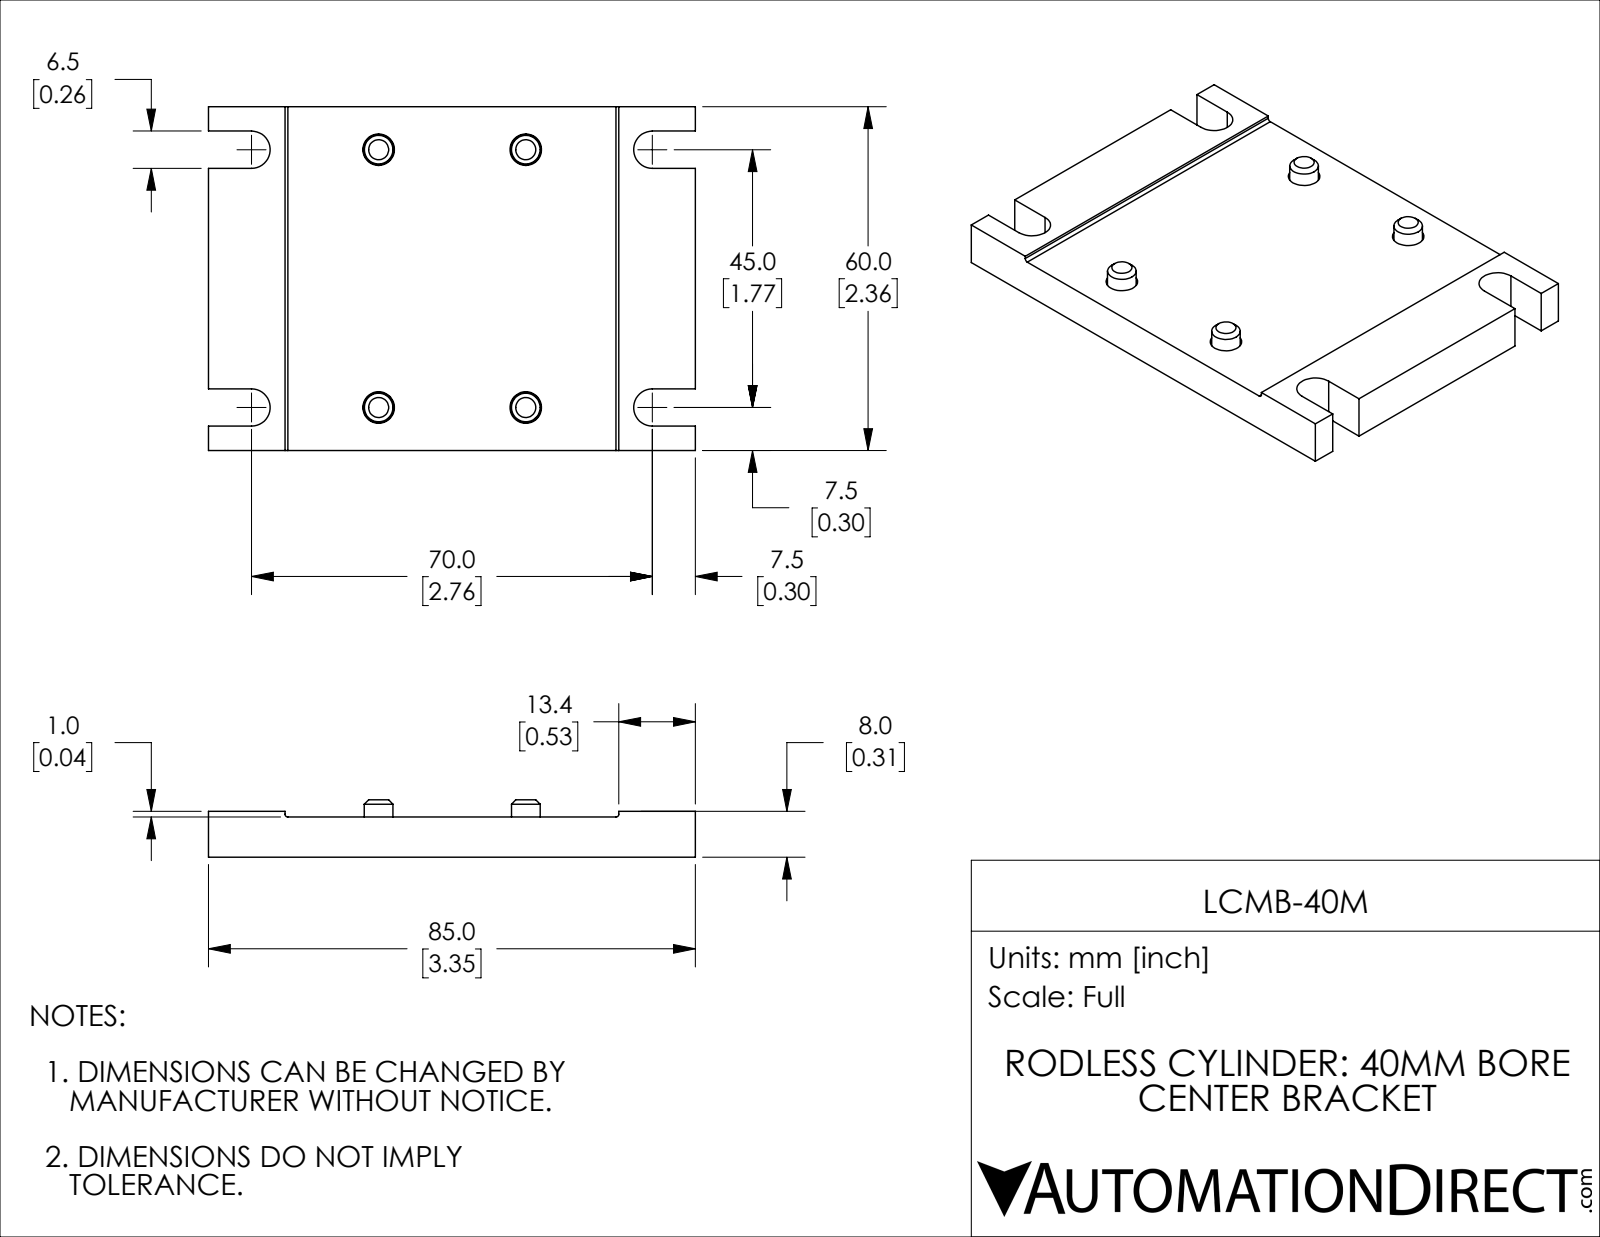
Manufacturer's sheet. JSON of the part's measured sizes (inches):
{"part_name": "LCMB-40M", "step_written_by": "SolidWorks 2019 (CONFIG_CONTROL_DESIGN)", "units": "inches", "bodies": {"solids": 5, "faces": 192, "planar": 114, "cylindrical": 38, "other": 40}, "overall_size": [3.346, 2.362, 0.394], "volume_in3": 2.149, "surface_area_in2": 21.76, "round_holes": [[0.217, 4]], "round_bosses_or_shafts": [[0.366, 4], [0.197, 4], [0.178, 4]], "partial_cylinders_radius": [[0.128, 4], [0.02, 2]], "face_to_face_distances": [0.276, 0.315, 0.039, 2.362, 3.346, 1.772, 0.167, 0.423, 1.939, 2.195], "hole_center_spacings": [1.012, 1.772, 2.04]}
